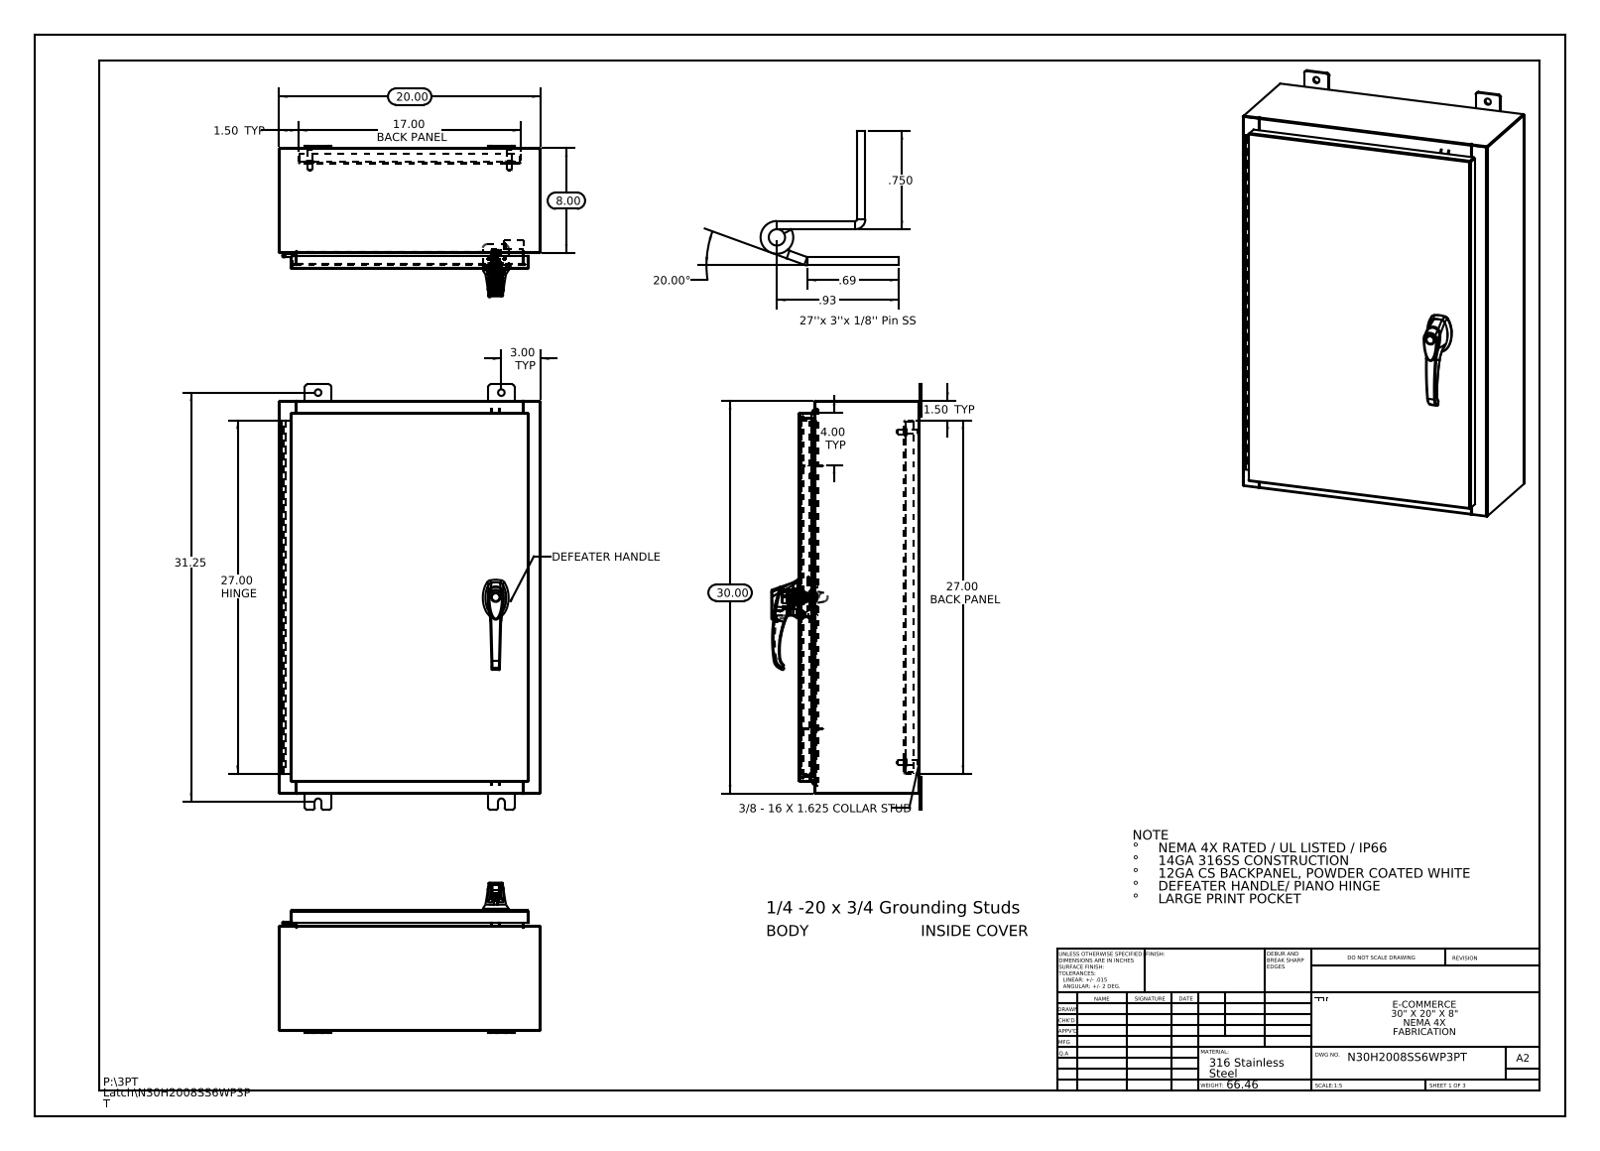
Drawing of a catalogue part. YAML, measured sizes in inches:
part_name: "N30H2008SS6WP3PT Hinge Cover Side; 033060_032151; 297025; 012103_012102 (+8 more)"
step_written_by: "SolidWorks 2013 (CONFIG_CONTROL_DESIGN)"
units: inches
bodies: {solids: 31, faces: 2576, planar: 953, cylindrical: 969, other: 654}
overall_size: [32.5, 20, 11.495]
volume: 236.3
surface_area: 5841
round_holes:
  - {diameter: 0.5, count: 8}
  - {diameter: 0.25, count: 4}
  - {diameter: 0.138, count: 3}
  - {diameter: 0.161, count: 3}
  - {diameter: 0.079, count: 2}
  - {diameter: 0.203, count: 2}
  - {diameter: 0.313, count: 2}
  - {diameter: 0.437, count: 2}
  - {diameter: 0.125, count: 1}
  - {diameter: 0.125, count: 1}
  - {diameter: 0.197, count: 1}
  - {diameter: 0.276, count: 1}
round_bosses_or_shafts:
  - {diameter: 0.625, count: 4}
  - {diameter: 0.375, count: 4}
  - {diameter: 0.33, count: 4}
  - {diameter: 1.181, count: 1}
  - {diameter: 0.748, count: 1}
  - {diameter: 0.68, count: 1}
  - {diameter: 0.661, count: 1}
  - {diameter: 0.639, count: 1}
partial_cylinders:
  - {radius: 0.118, count: 37}
  - {radius: 0.006, count: 33}
  - {radius: 0.013, count: 24}
  - {radius: 0.19, count: 24}
  - {radius: 0.088, count: 18}
  - {radius: 0.039, count: 15}
  - {radius: 0.028, count: 12}
  - {radius: 0.008, count: 6}
face_to_face_distances: [0.075, 9.126, 0.104, 9.051, 9.201, 19.925, 1, 1.075, 8.051, 8.126]
hole_center_spacings: [8.369, 15.143, 0.295, 0.625, 0.841, 1.25, 1.313, 1.561]
